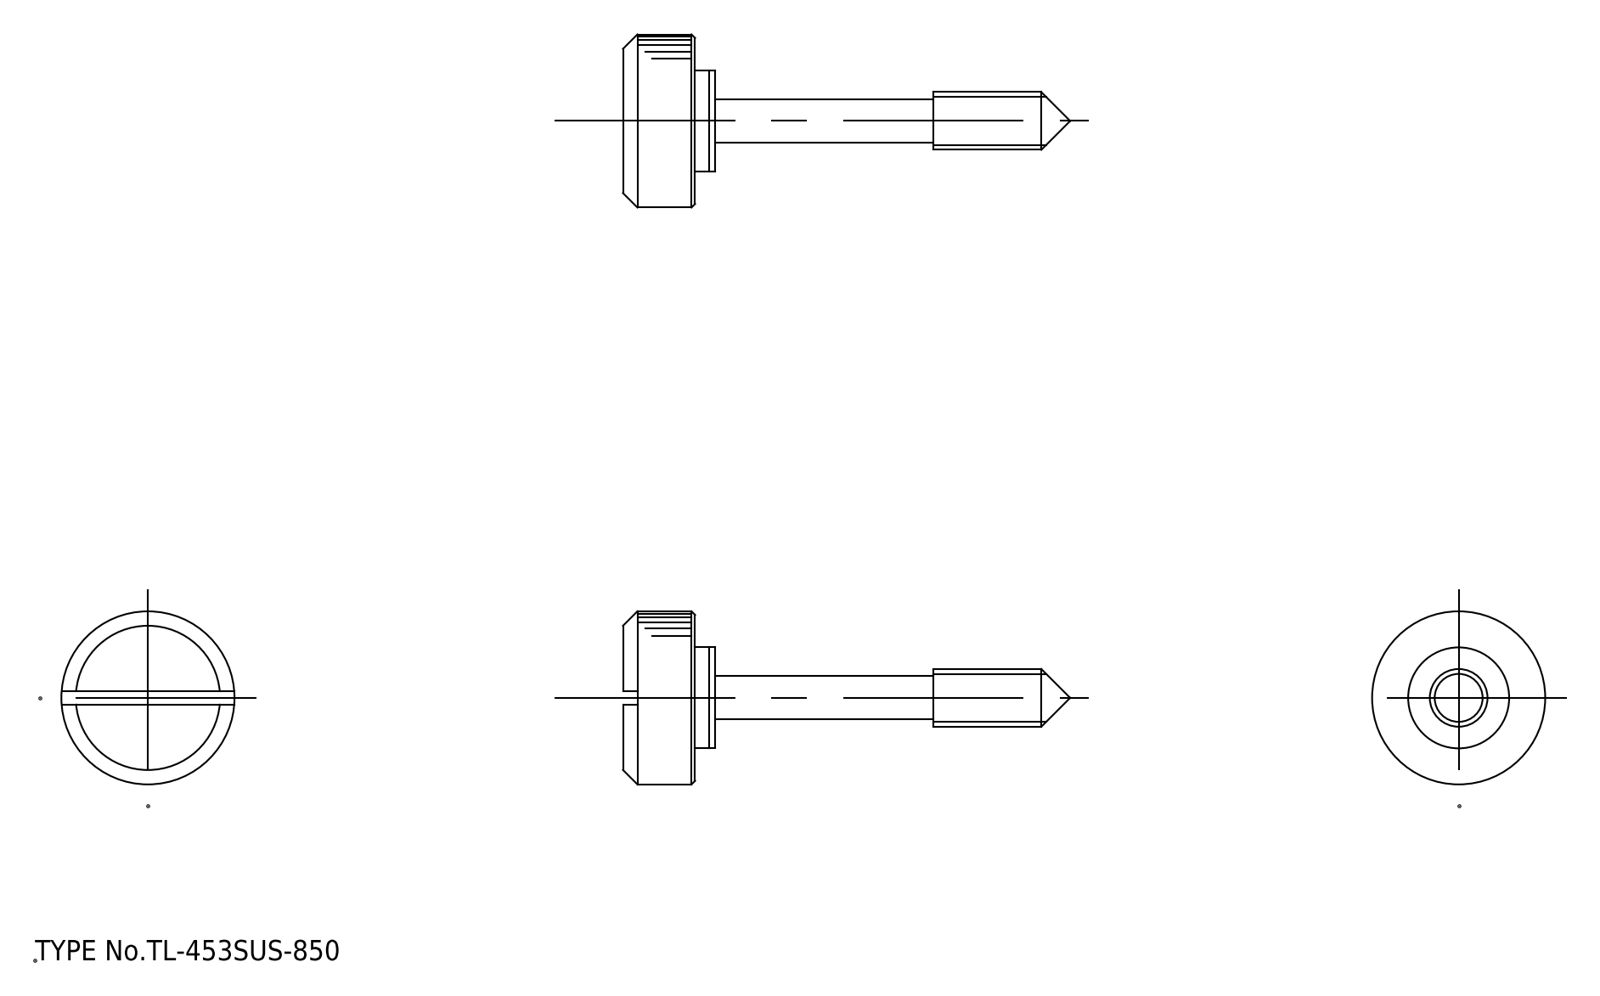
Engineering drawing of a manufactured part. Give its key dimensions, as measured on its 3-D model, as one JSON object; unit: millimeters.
{"part_name": "washer; knob", "step_written_by": "spGate 19.8.4 (****-****-****-****) (AUTOMOTIVE_DESIGN)", "units": "millimeters", "bodies": {"solids": 2, "faces": 42, "planar": 18, "cylindrical": 18, "other": 6}, "overall_size": [62, 24, 24], "volume_mm3": 6387, "surface_area_mm2": 3017, "round_bosses_or_shafts": [[24, 1], [14, 1], [8, 1], [6, 1]], "partial_cylinders_radius": [[1.25, 4], [3.05, 1]], "face_to_face_distances": [10, 2, 12, 12.8, 2.8, 0.8, 1.8, 8, 10.8, 43]}
